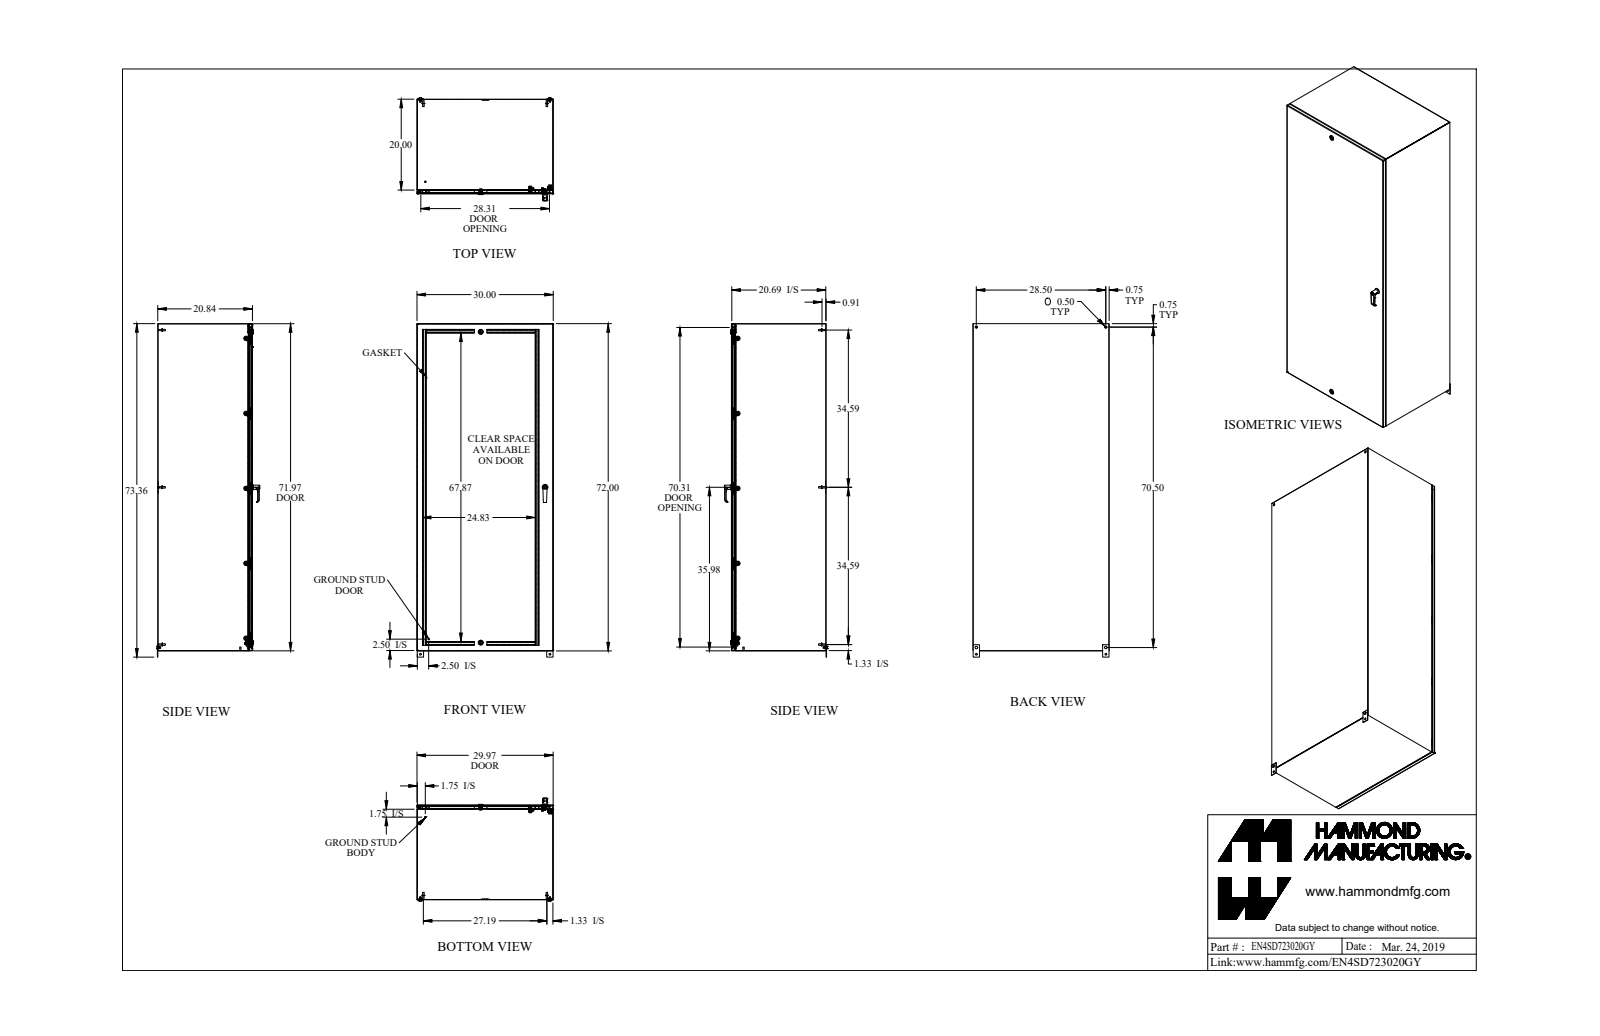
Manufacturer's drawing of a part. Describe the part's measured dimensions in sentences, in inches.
The part is named "EN4SD723020GY". Its 3-D file was written by "SolidWorks 2018 (AUTOMOTIVE_DESIGN)". It is 98 solids with 2429 faces: 1159 planar, 890 cylindrical and 380 other. Overall it measures 73.363 by 30 by 22.693 inches. Its volume is 690.7 cubic inches and its surface area 19 378 square inches. Round holes: 10 of diameter 0.176, 6 of diameter 0.196, 5 of diameter 0.25, 5 of diameter 0.265, 5 of diameter 0.413, 4 of diameter 0.256, 4 of diameter 0.313, 4 of diameter 0.39, 4 of diameter 0.394, 4 of diameter 0.5, 2 of diameter 0.232, 2 of diameter 0.307. Round bosses or shafts: 11 of diameter 0.25, 10 of diameter 0.156, 9 of diameter 0.375, 7 of diameter 0.625, 6 of diameter 0.313, 6 of diameter 0.27, 5 of diameter 1, 4 of diameter 0.63. Partial cylindrical surfaces (rounded edges, fillets, slot ends): 24 of radius 0.043, 23 of radius 0.062, 17 of radius 0.036, 17 of radius 0.108, 15 of radius 0.03, 14 of radius 0.125, 10 of radius 0.006, 10 of radius 0.094. The main face-to-face distances are 0.072, 20.765, 29.928, 20.693, 20.837, 29.856, 30, 71.928, 71.856, 72. The hole center spacings are 16.487, 28.5, 33, 0.787, 1.5, 13.313, 14.208, 15.267.
